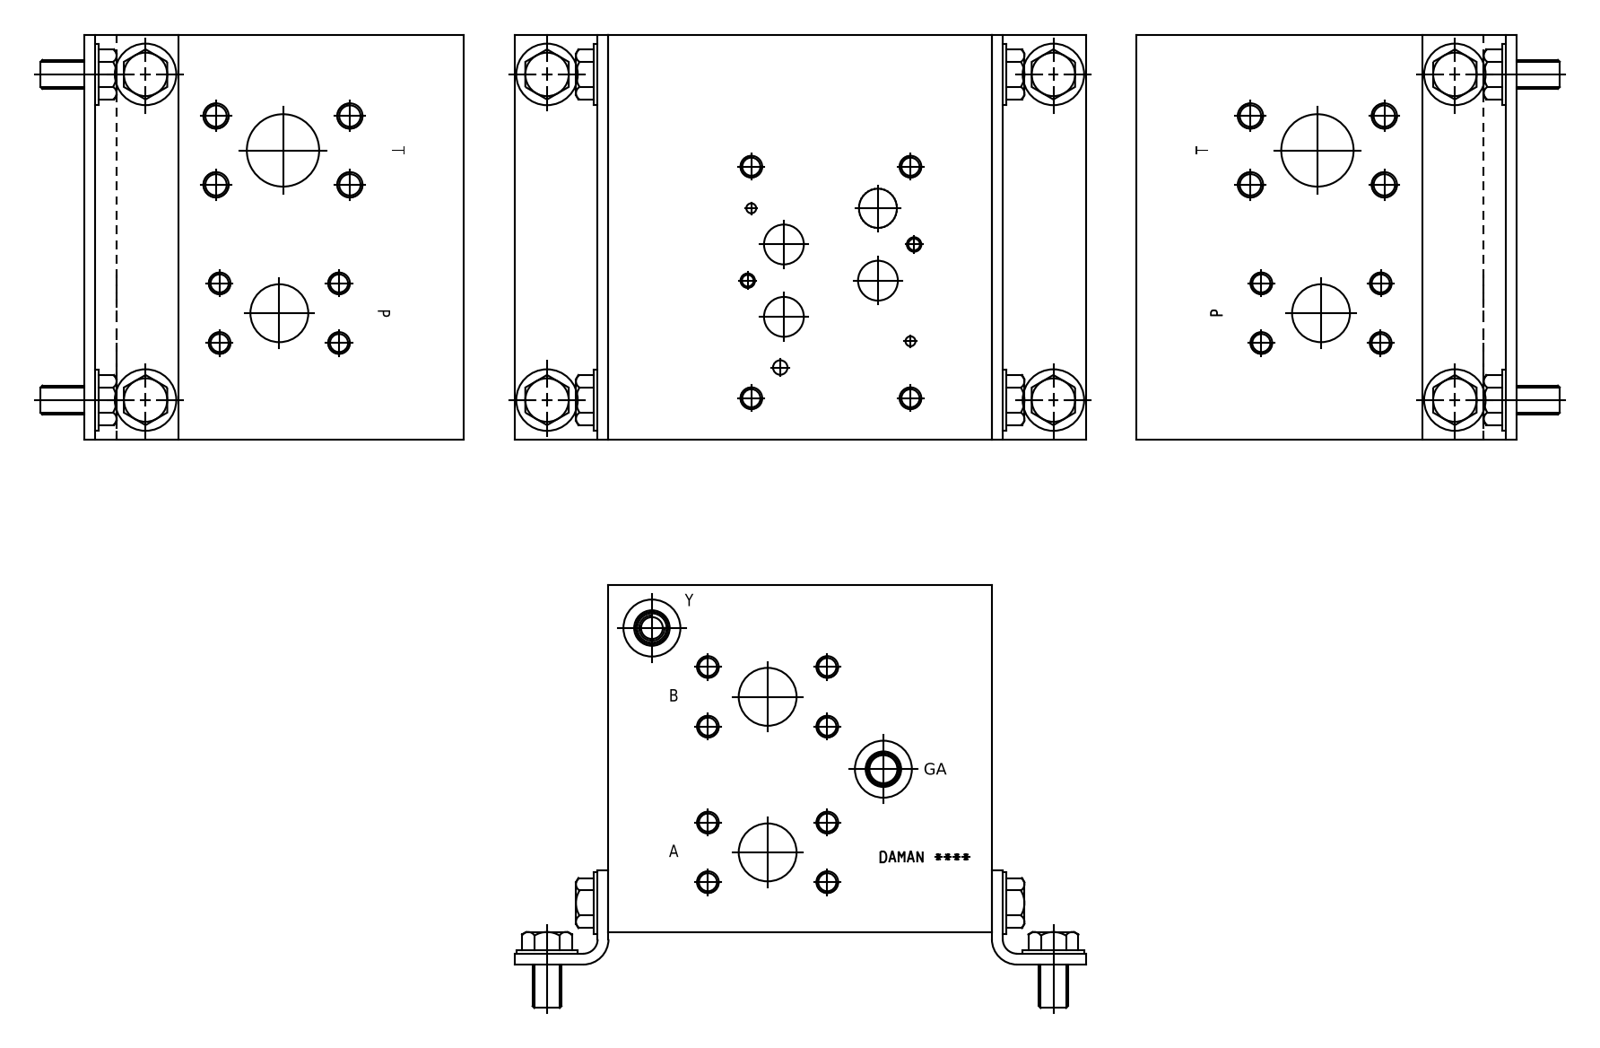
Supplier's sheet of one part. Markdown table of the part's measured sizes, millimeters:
| quantity | value |
| --- | --- |
| part name | Part_AD07HP014F_3D |
| STEP written by | Autodesk Inventor 2021 (AUTOMOTIVE_DESIGN) |
| units | millimeters |
| bodies | 1 solid, 613 faces (374 planar, 91 cylindrical, 148 other) |
| overall size | 177.8 × 168.28 × 152.4 |
| volume | 4 427 000 mm³ |
| surface area | 204 797 mm² |
| round holes (diameter × count) | 9.53 × 19, 7.92 × 18, 9.35 × 6, 11.13 × 6, 6.35 × 3, 17.48 × 3, 25.4 × 3, 4.37 × 2, 5.11 × 2, 10.72 × 2, 12.7 × 2, 12.9 × 2 |
| main face-to-face distances | 152.4, 168.28, 177.8, 0.79, 177.01, 25.4, 3.05, 28.45, 139.83, 25.36 |
| hole center spacings | 26.17, 29.27, 29.28, 52.38, 58.55, 58.73, 68.25, 66.03 |
